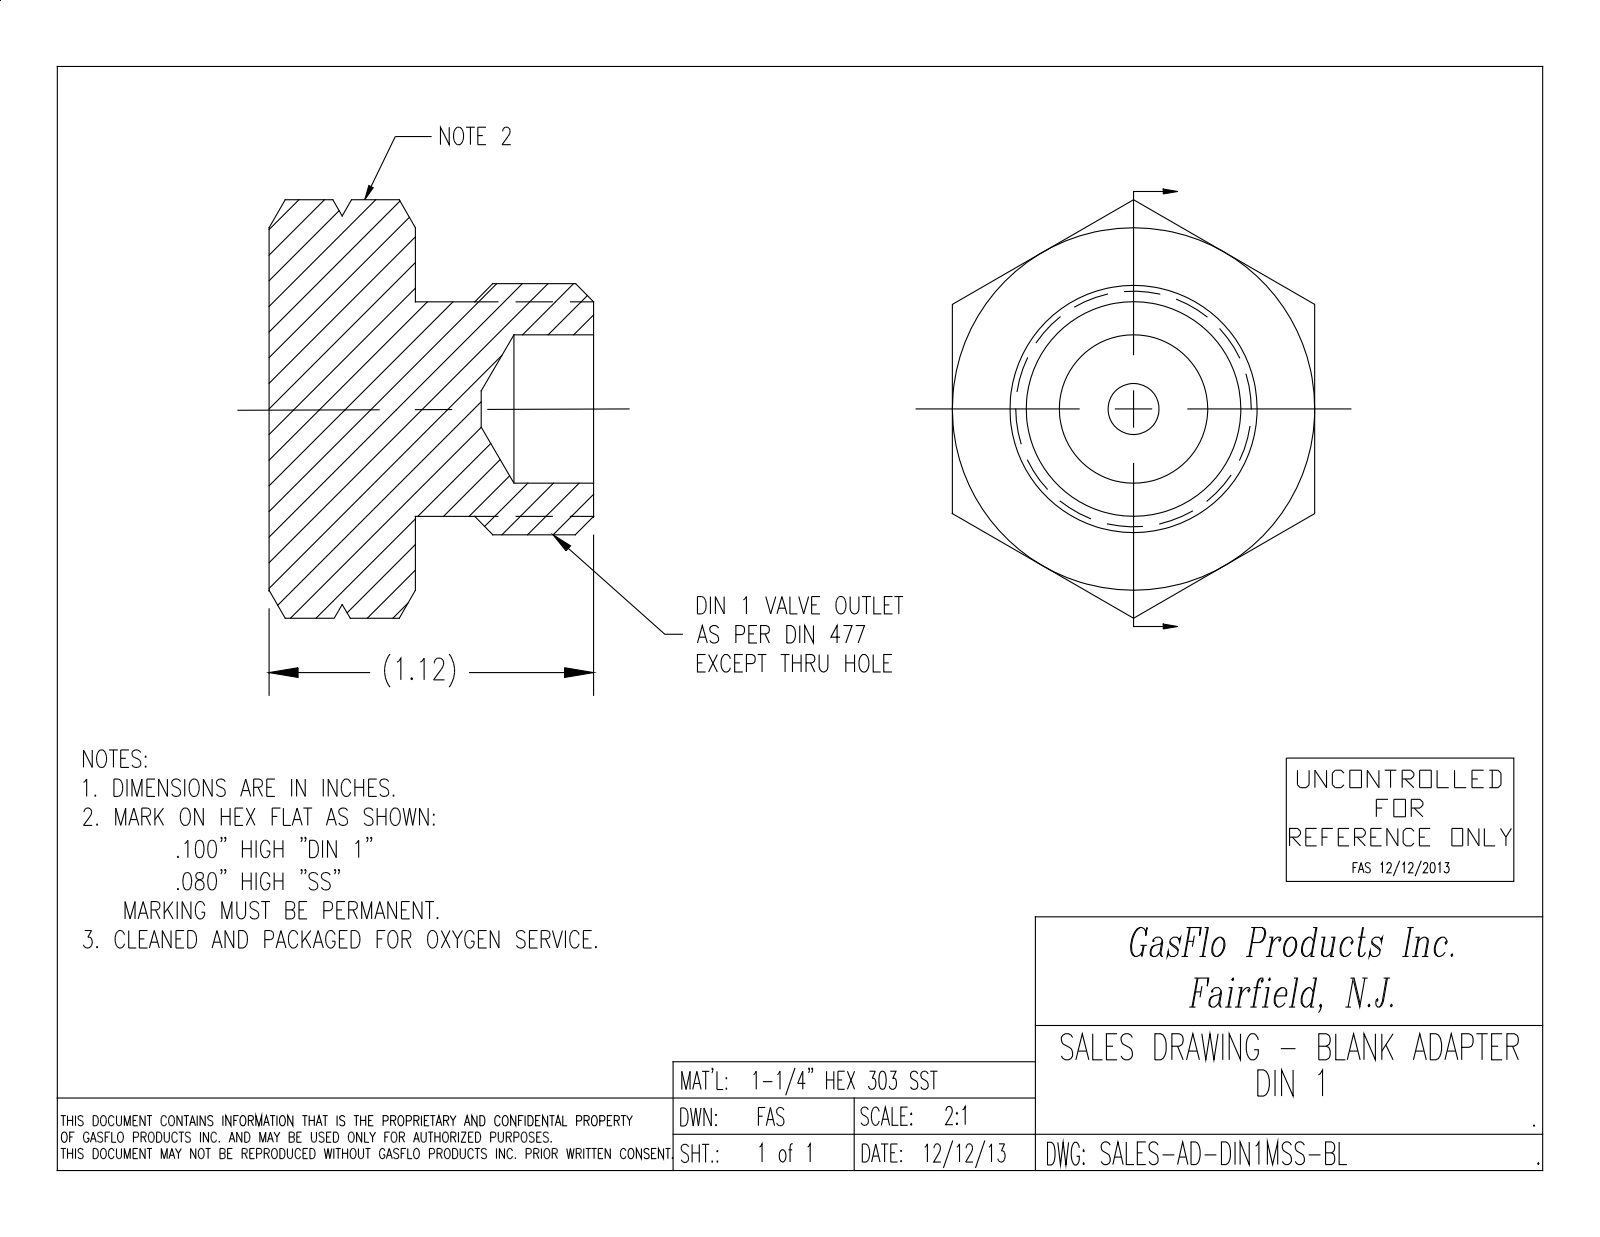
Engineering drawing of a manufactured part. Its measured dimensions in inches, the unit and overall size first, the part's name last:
Units: inches
Overall size (bounding box): 1.443 × 1.25 × 1.12
Round holes (diameter × count): ⌀0.512 ×1
Round bosses / shafts (diameter × count): ⌀0.85 ×1, ⌀0.74 ×1
Main face-to-face distances: 1.25, 0.505, 1.12, 0.615, 0.729, 0.224, 0.391, 1.245, 0.081, 0.078
Volume: 0.902 in³ · Surface area: 7.573 in²
Bodies: 1 solid, 126 faces (47 planar, 14 cylindrical, 65 other)
Part name (STEP PRODUCT): AD-DIN1MSS-BL
STEP written by: SolidWorks 2018 (CONFIG_CONTROL_DESIGN)
